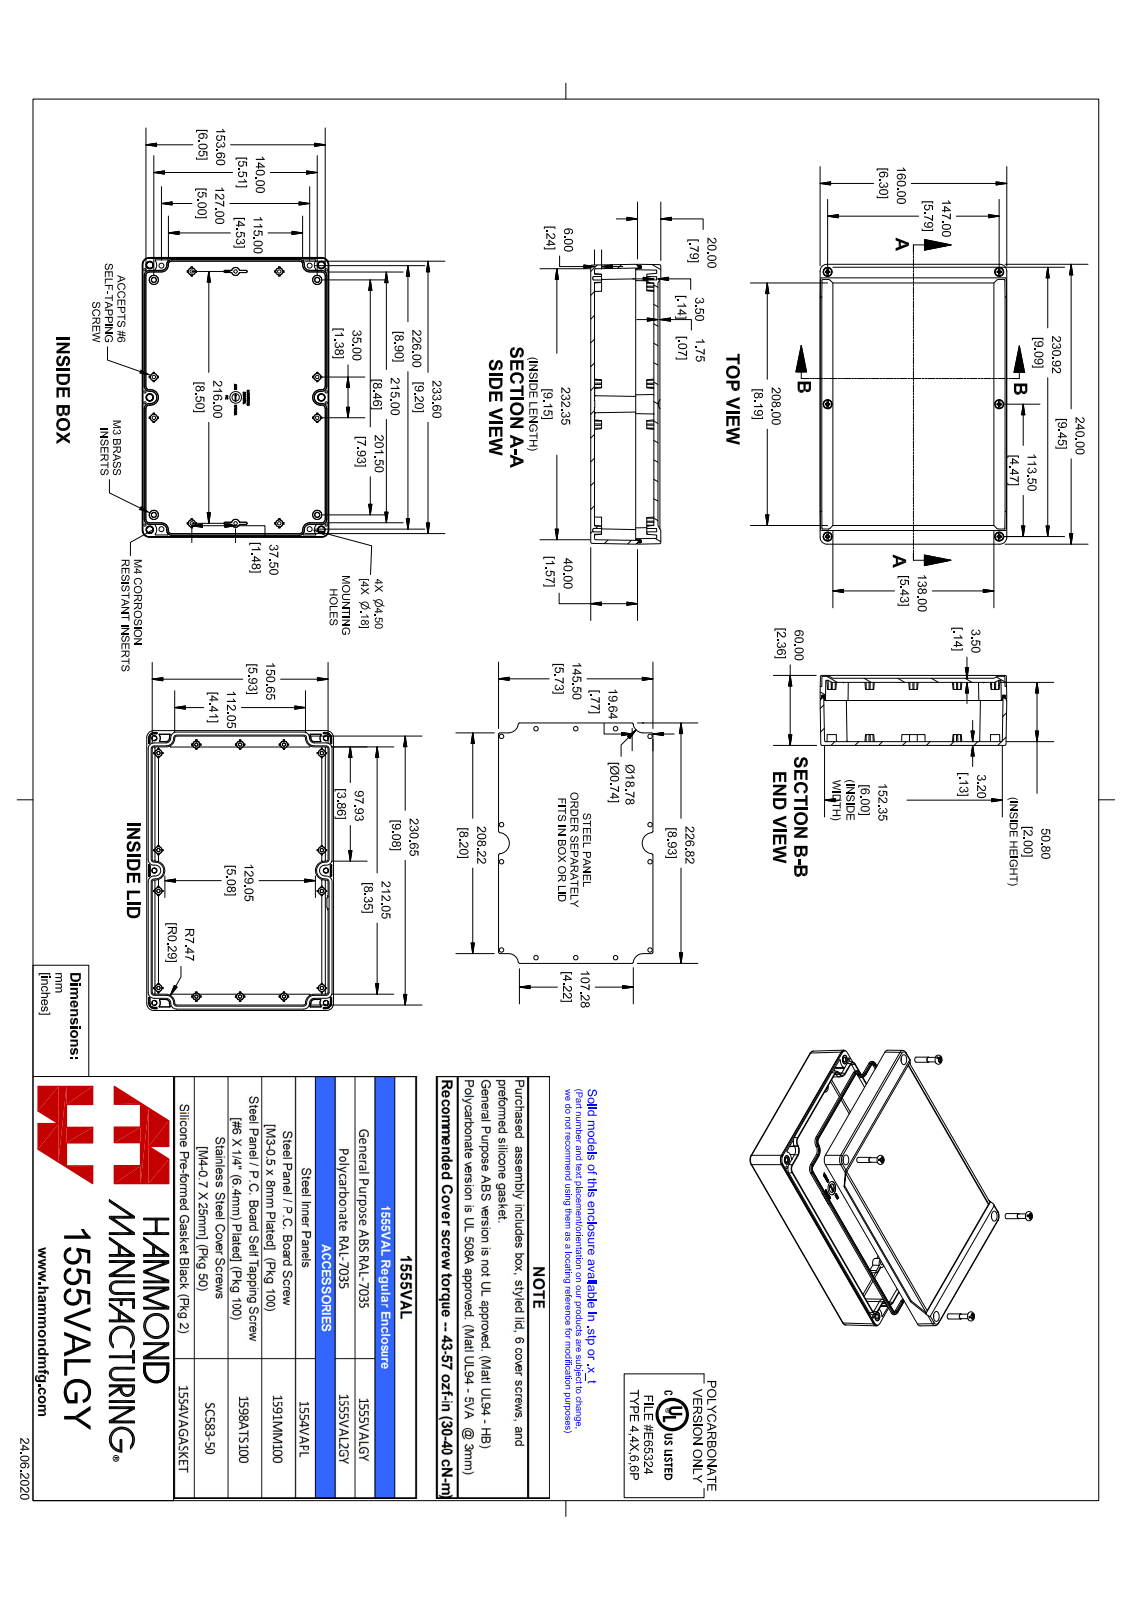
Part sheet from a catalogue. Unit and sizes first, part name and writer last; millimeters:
Units: millimetres
Overall size (bounding box): 240 × 160 × 60
Round holes (diameter × count): ⌀3.3 ×6, ⌀2.5 ×4, ⌀4.6 ×4
Round bosses / shafts (diameter × count): ⌀6.9 ×6, ⌀6.4 ×6, ⌀5.5 ×6, ⌀5.3 ×6, ⌀3.9 ×6, ⌀3.5 ×6, ⌀4.8 ×4, ⌀3.9 ×4
Partial cylindrical surfaces — rounded edges, fillets, slot ends (radius × count): R0.5 ×47, R0.3 ×28, R1 ×22, R2.5 ×12, R5 ×12, R1.5 ×8, R6 ×8, R0.8 ×6
Main face-to-face distances: 3.2, 3.5, 50.8, 54, 57.5, 54.3, 4.7, 155.3, 152.1, 240
Hole centre spacings: 13.2, 100.8, 113.5, 144.1, 175.3, 185.7, 214.3, 257.9
Volume: 431 100 mm³ · Surface area: 281 700 mm²
Bodies: 19 solids, 2398 faces (926 planar, 468 cylindrical, 1004 other)
Part name (STEP PRODUCT): 1555VALGY
STEP written by: SolidWorks 2021 (AUTOMOTIVE_DESIGN)
